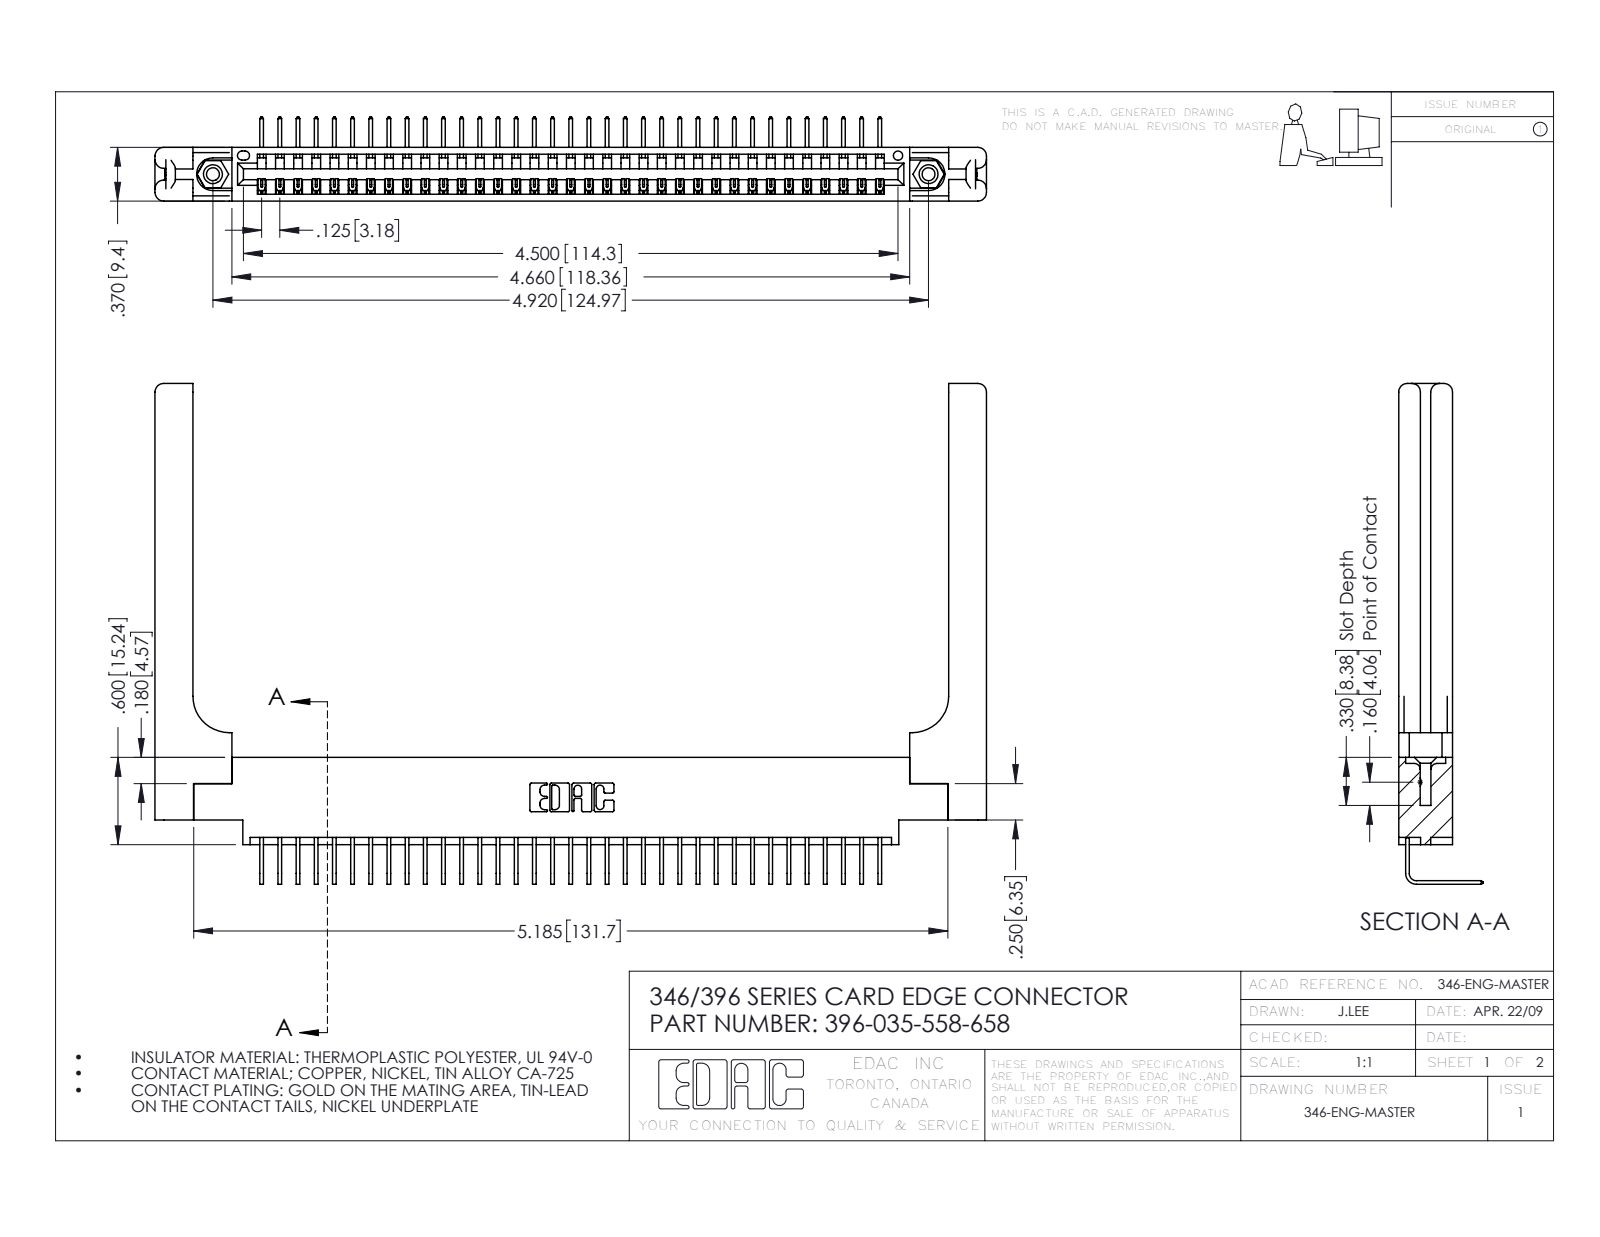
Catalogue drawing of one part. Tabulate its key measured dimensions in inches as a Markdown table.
| quantity | value |
| --- | --- |
| part name | 346-220-058_345-220-058; 345-292-001_558 Tail - 2; 346 Part_0.170 Offset - 0.156 Dia-TH; 345-250-001_345-250-001-102 (+1 more) |
| STEP written by | SolidWorks 2016 (CONFIG_CONTROL_DESIGN) |
| units | inches |
| bodies | 40 solids, 2482 faces (1698 planar, 724 cylindrical, 60 other) |
| overall size | 5.716 × 3.443 × 0.58 |
| volume | 1.302 in³ |
| surface area | 35.98 in² |
| round holes (diameter × count) | 0.089 × 2, 0.125 × 2, 0.156 × 2, 0.064 × 1 |
| round bosses / shafts (diameter × count) | 0.155 × 2 |
| partial cylindrical surfaces (radius × count) | 0.006 × 70, 0.01 × 22, 0.06 × 16, 0.007 × 6, 0.031 × 6, 0.026 × 3, 0.03 × 2, 0.031 × 2 |
| main face-to-face distances | 0.37, 0.322, 0.048, 0.072, 0.148, 0.15, 0.025, 0.298, 0.25, 0.222 |
| hole center spacings | 0.246, 4.711, 4.92 |
